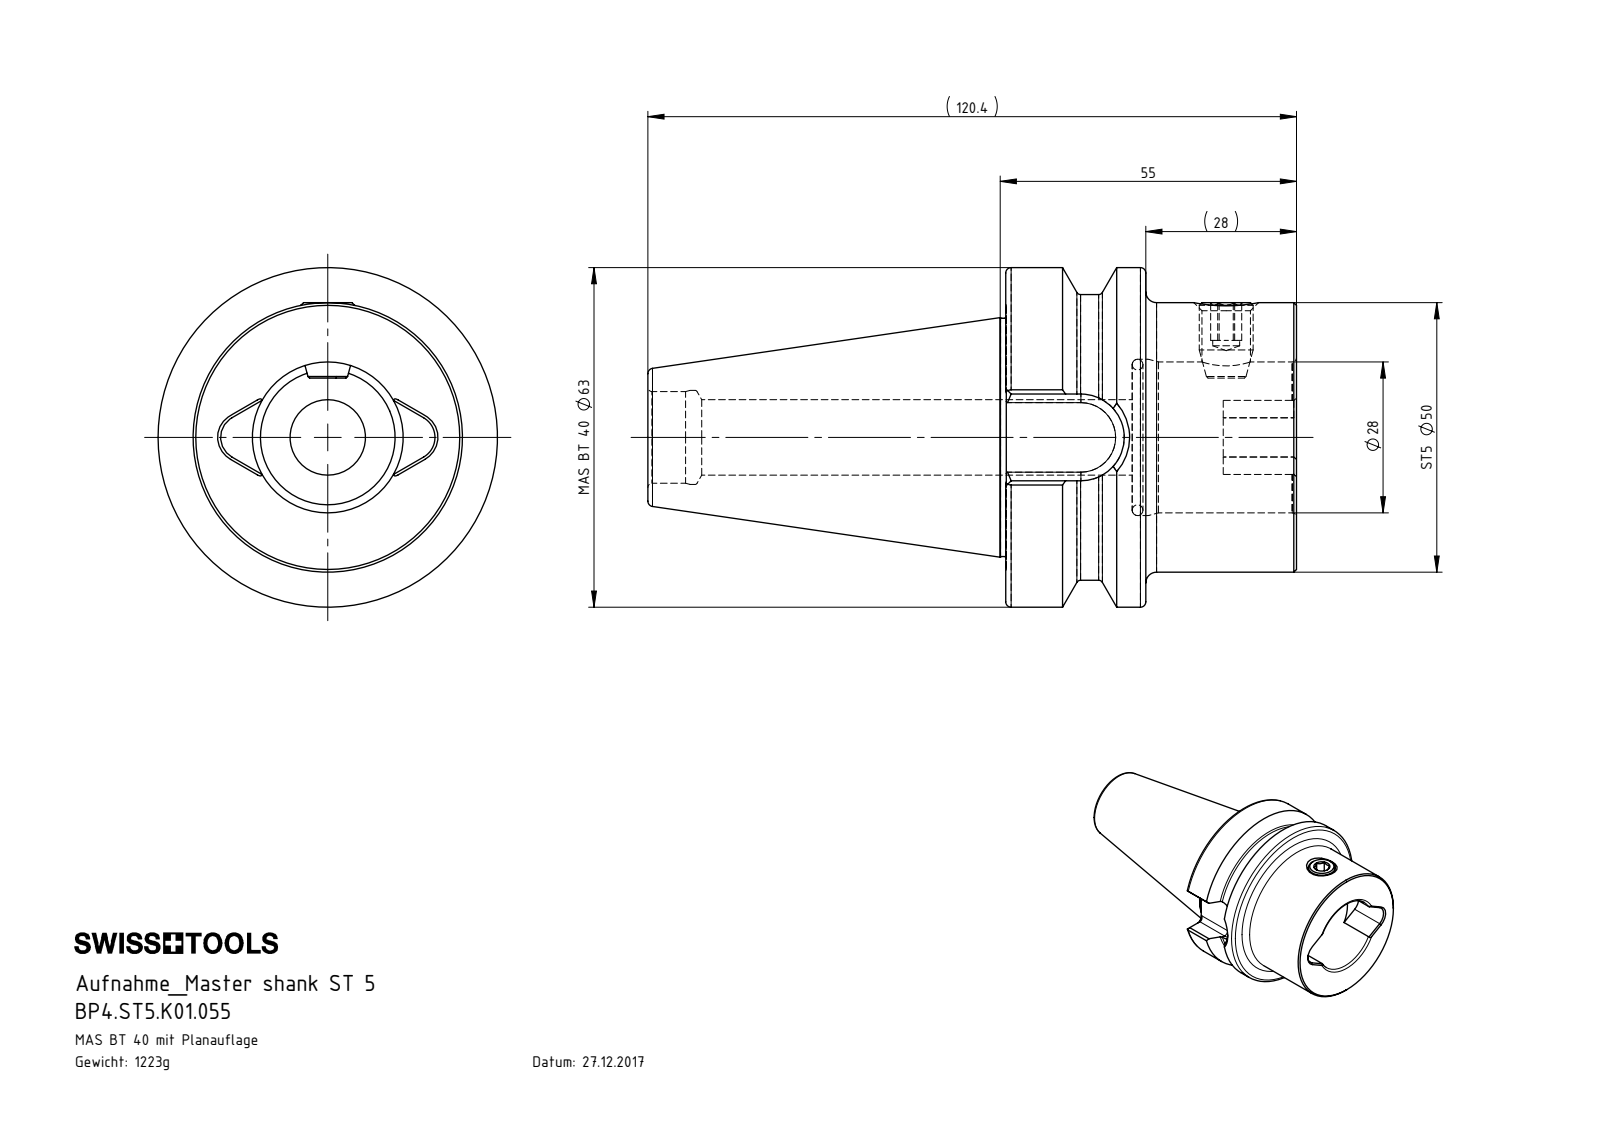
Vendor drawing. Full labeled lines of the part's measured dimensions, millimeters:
Part name (STEP PRODUCT): BP4.ST5.K01.055; DIN 3771 - 25x2; ST5-ER1.001.012_A
STEP written by: SolidWorks 2017 (AUTOMOTIVE_DESIGN)
Units: millimetres
Bodies: 3 solids, 158 faces (44 planar, 42 cylindrical, 72 other)
Overall size (bounding box): 120.4 × 63 × 63
Volume: 155 968 mm³ · Surface area: 30 635 mm²
Round holes (diameter × count): ⌀5 ×1, ⌀9 ×1, ⌀14 ×1, ⌀17 ×1, ⌀17.45 ×1, ⌀28 ×1, ⌀29 ×1
Round bosses / shafts (diameter × count): ⌀63 ×1, ⌀53 ×1, ⌀50 ×1, ⌀44.45 ×1, ⌀44.2 ×1, ⌀10 ×1
Partial cylindrical surfaces — rounded edges, fillets, slot ends (radius × count): R1.6 ×8, R4.2 ×2, R8.05 ×1
Main face-to-face distances: 53.97, 26, 27.97, 23.47, 2.53, 30.5, 45, 23.37, 25.9, 53.87
